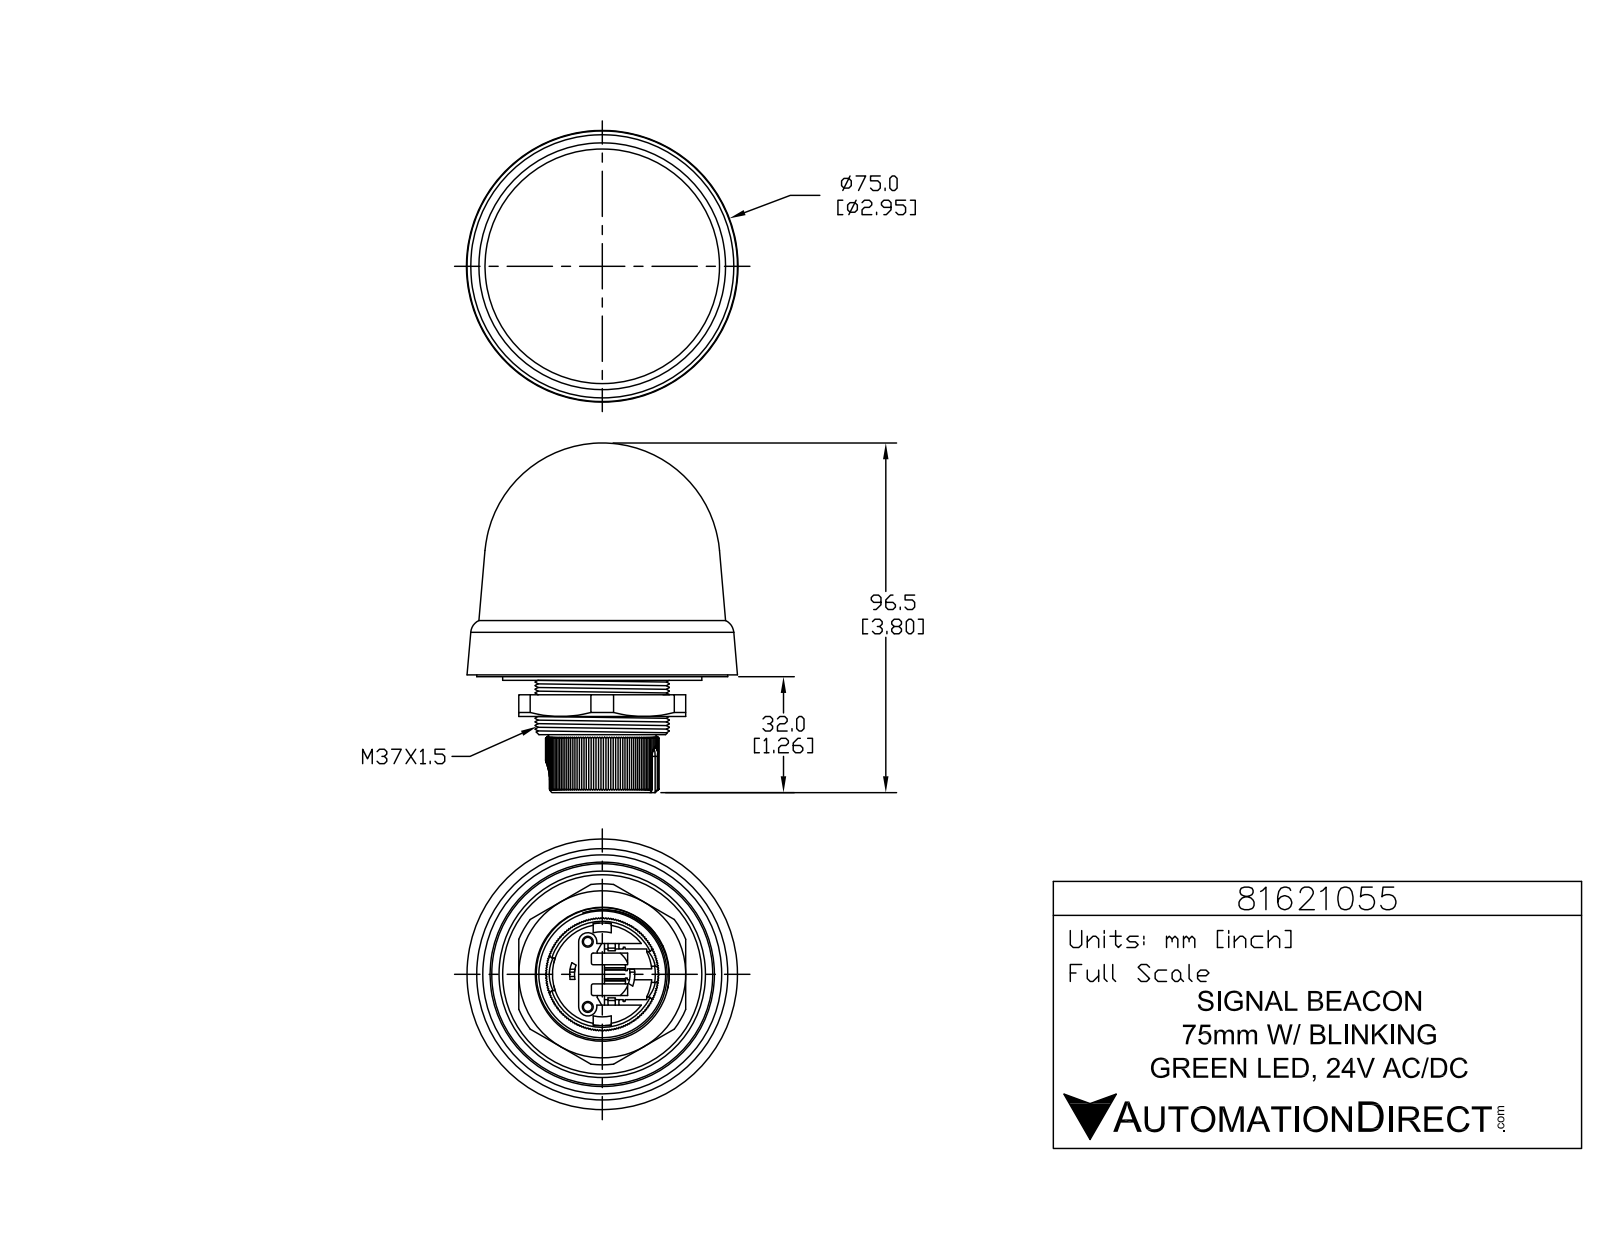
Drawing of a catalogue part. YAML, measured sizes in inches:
part_name: "81621055"
step_written_by: "SolidWorks 2019 (CONFIG_CONTROL_DESIGN)"
units: inches
bodies: {solids: 3, faces: 560, planar: 432, cylindrical: 80, other: 48}
overall_size: [3.799, 2.941, 2.941]
volume: 12.36
surface_area: 58.68
round_holes:
  - {diameter: 0.094, count: 2}
  - {diameter: 0.118, count: 2}
  - {diameter: 0.604, count: 1}
  - {diameter: 1.142, count: 1}
round_bosses_or_shafts:
  - {diameter: 0.217, count: 2}
  - {diameter: 0.067, count: 2}
  - {diameter: 2.165, count: 1}
  - {diameter: 1.457, count: 1}
  - {diameter: 0.925, count: 1}
partial_cylinders:
  - {radius: 0.008, count: 6}
  - {radius: 0.039, count: 6}
  - {radius: 0.02, count: 4}
  - {radius: 0.031, count: 2}
  - {radius: 0.079, count: 2}
  - {radius: 0.098, count: 2}
  - {radius: 0.177, count: 1}
  - {radius: 0.354, count: 1}
face_to_face_distances: [0.177, 0.354, 0.197, 0.433, 0.512, 0.335, 0.059, 0.394, 0.118, 0.157]
hole_center_spacings: [0.388, 0.709]
